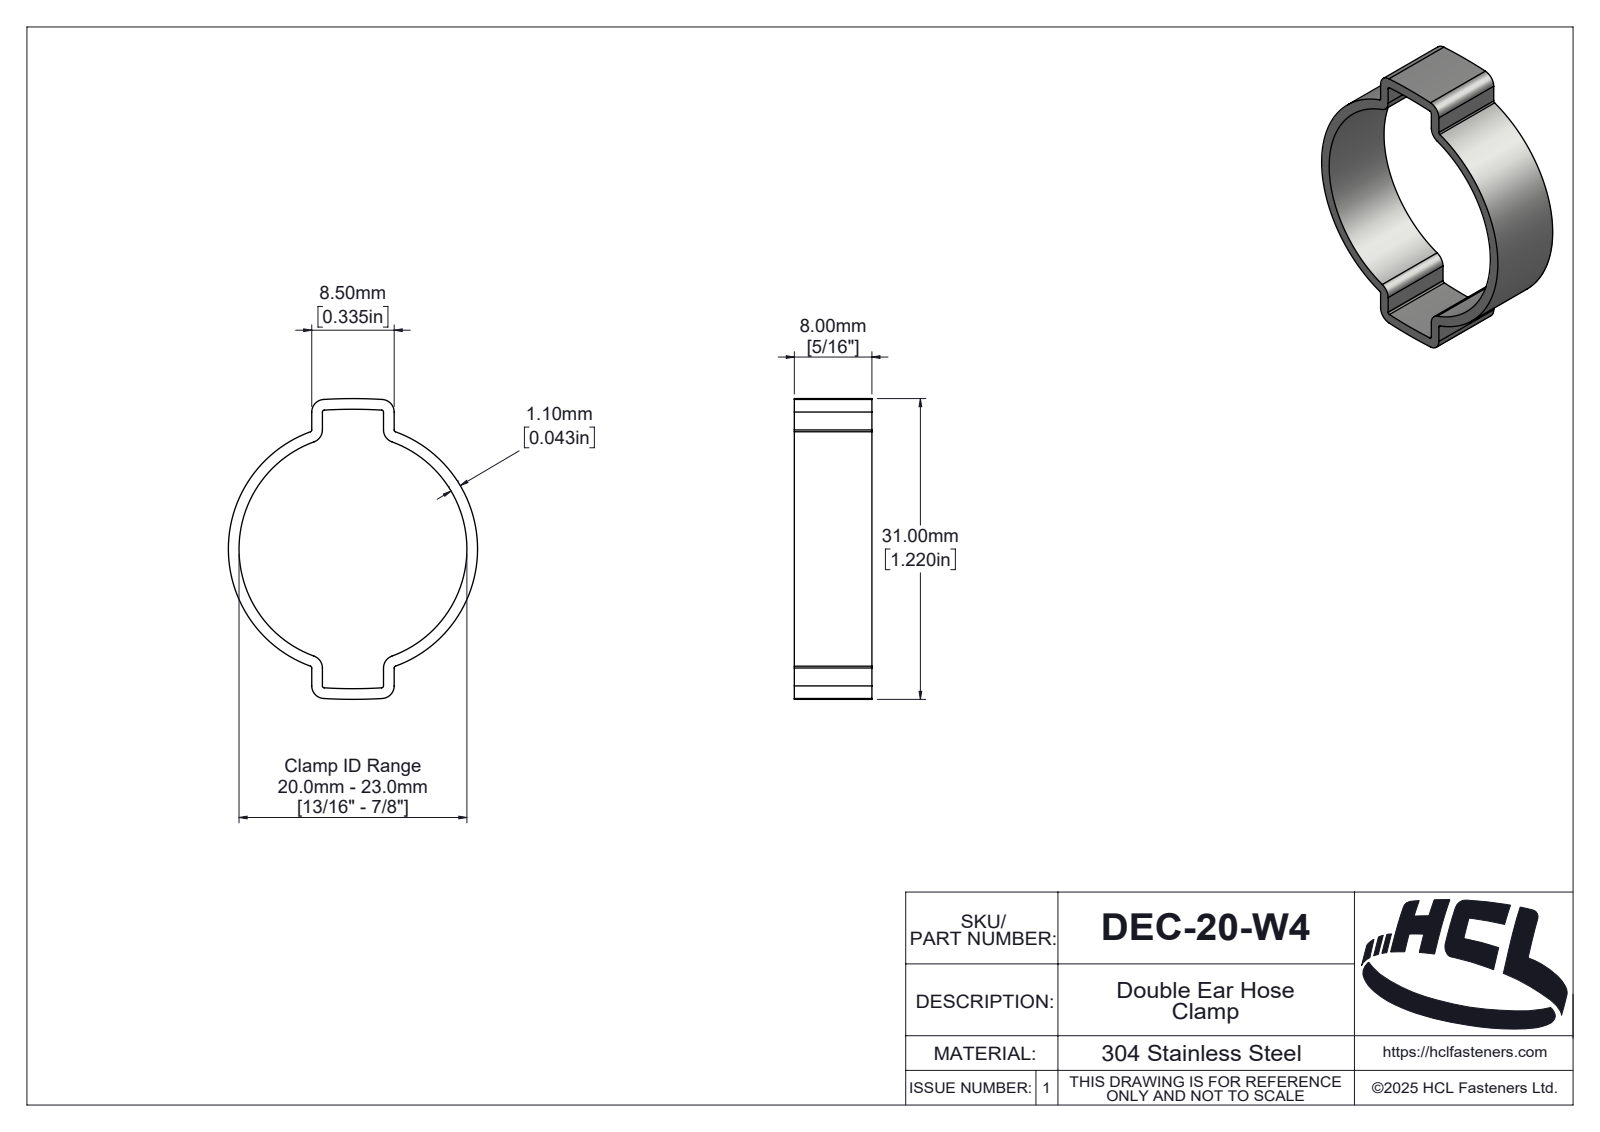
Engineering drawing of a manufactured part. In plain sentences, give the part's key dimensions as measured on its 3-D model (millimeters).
The part is named "DEC-20-W4". Its 3-D file was written by "SolidWorks 2025 (AUTOMOTIVE_DESIGN)". It is 1 solid with 137 faces: 12 planar, 67 cylindrical and 58 other. Overall it measures 31 by 25.7 by 8 millimeters. Its volume is 772 cubic millimeters and its surface area 1 600 square millimeters. Partial cylindrical surfaces (rounded edges, fillets, slot ends): 8 of radius 0.2, 8 of radius 1.3, 2 of radius 49.66, 2 of radius 50.76, 1 of radius 0.2, 1 of radius 0.81, 1 of radius 1.01, 1 of radius 1.06. The main face-to-face distances are 8, 1.1, 7.4, 8.5, 6.3, 4.13, 3.03, 3.27, 4.37, 3.98.
